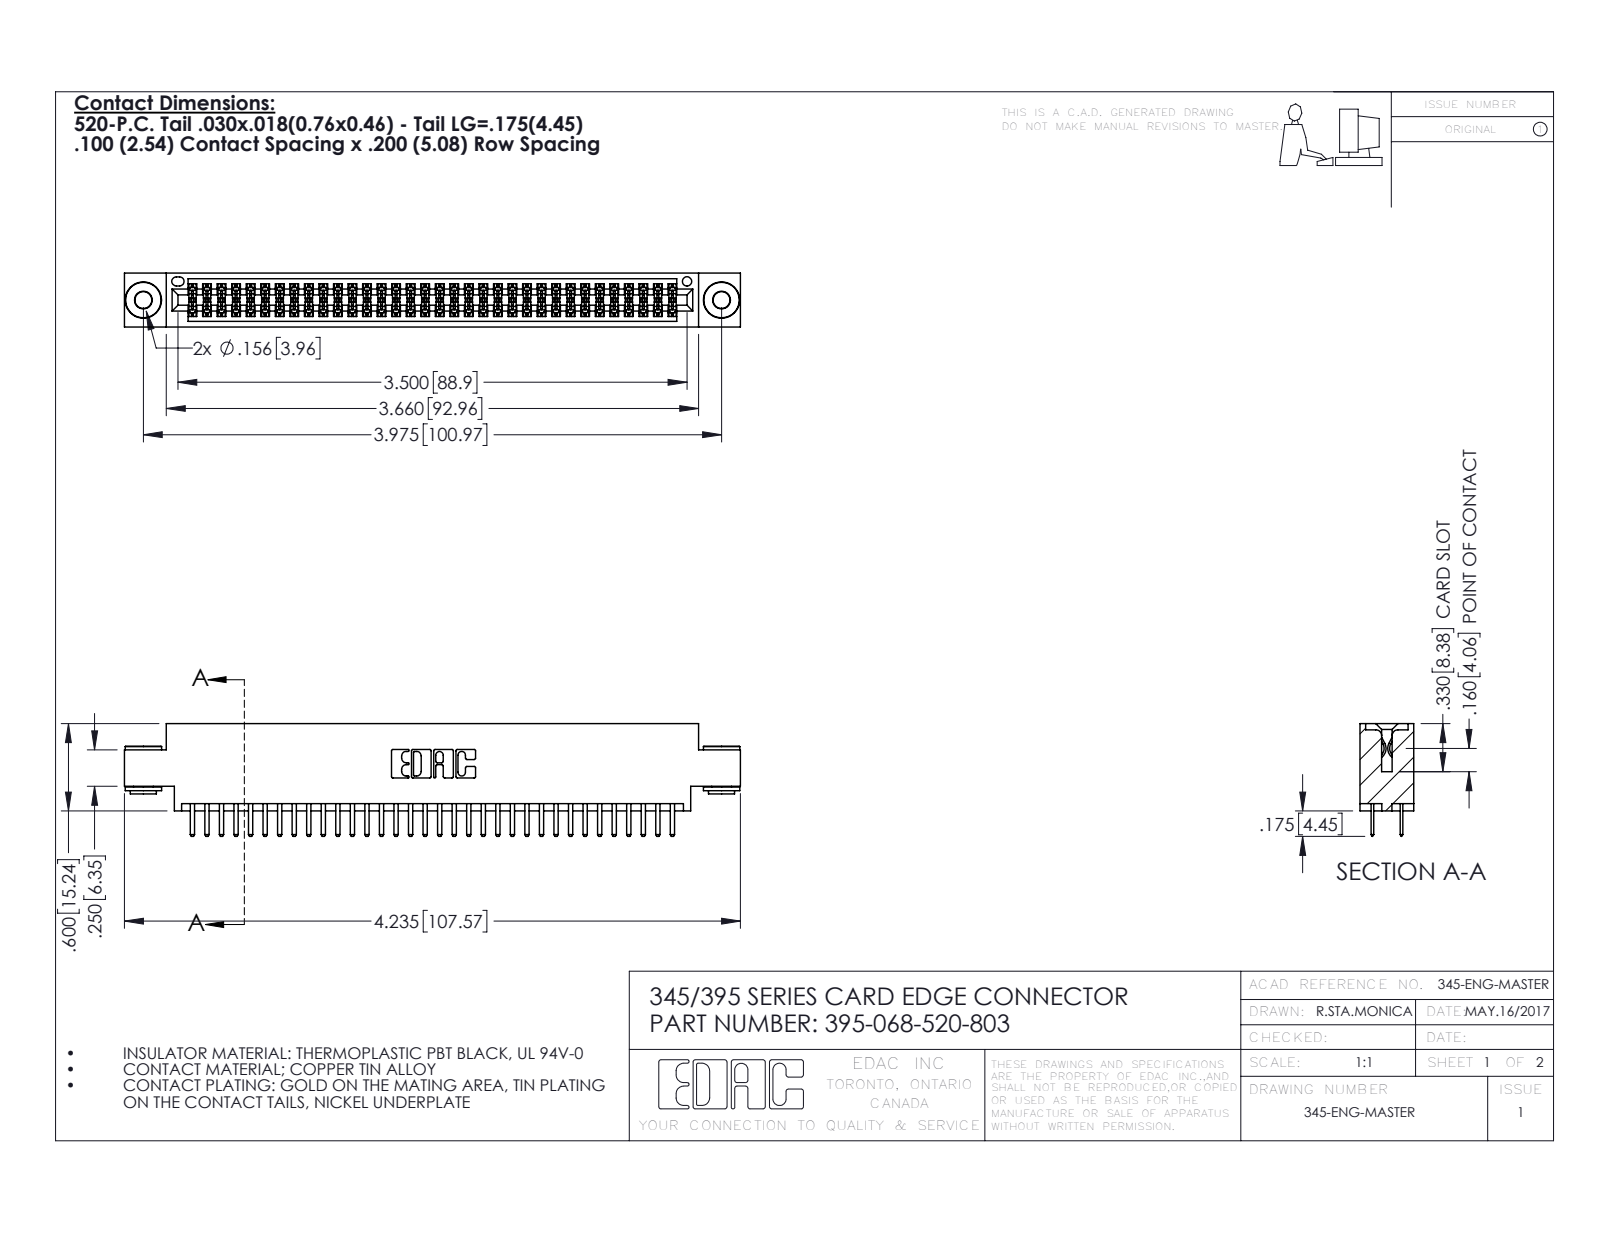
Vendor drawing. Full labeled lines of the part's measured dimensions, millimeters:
Part name (STEP PRODUCT): 345 Part_0.170 Offset - 0.156 Dia-TH; 395-068-520-803; 345-292-001_345-293-120; 345-250-002_345-250-002-102
STEP written by: SolidWorks 2016 (CONFIG_CONTROL_DESIGN)
Units: millimetres
Bodies: 71 solids, 3840 faces (2474 planar, 1358 cylindrical, 8 other)
Overall size (bounding box): 107.6 × 19.7 × 9.4
Volume: 10 300 mm³ · Surface area: 15 280 mm²
Round holes (diameter × count): ⌀2.9 ×2, ⌀4 ×2, ⌀1.6 ×1
Round bosses / shafts (diameter × count): ⌀6.4 ×2, ⌀4.6 ×2, ⌀3.5 ×2
Partial cylindrical surfaces — rounded edges, fillets, slot ends (radius × count): R0.2 ×102, R0.3 ×72, R0.3 ×22, R0.2 ×6, R0.8 ×6, R0.7 ×3, R0.4 ×2, R0.5 ×2
Main face-to-face distances: 1.8, 7.6, 5.1, 9.4, 2.5, 6.9, 0.6, 5.7, 4.4, 0.6
Hole centre spacings: 6.9, 95, 101
